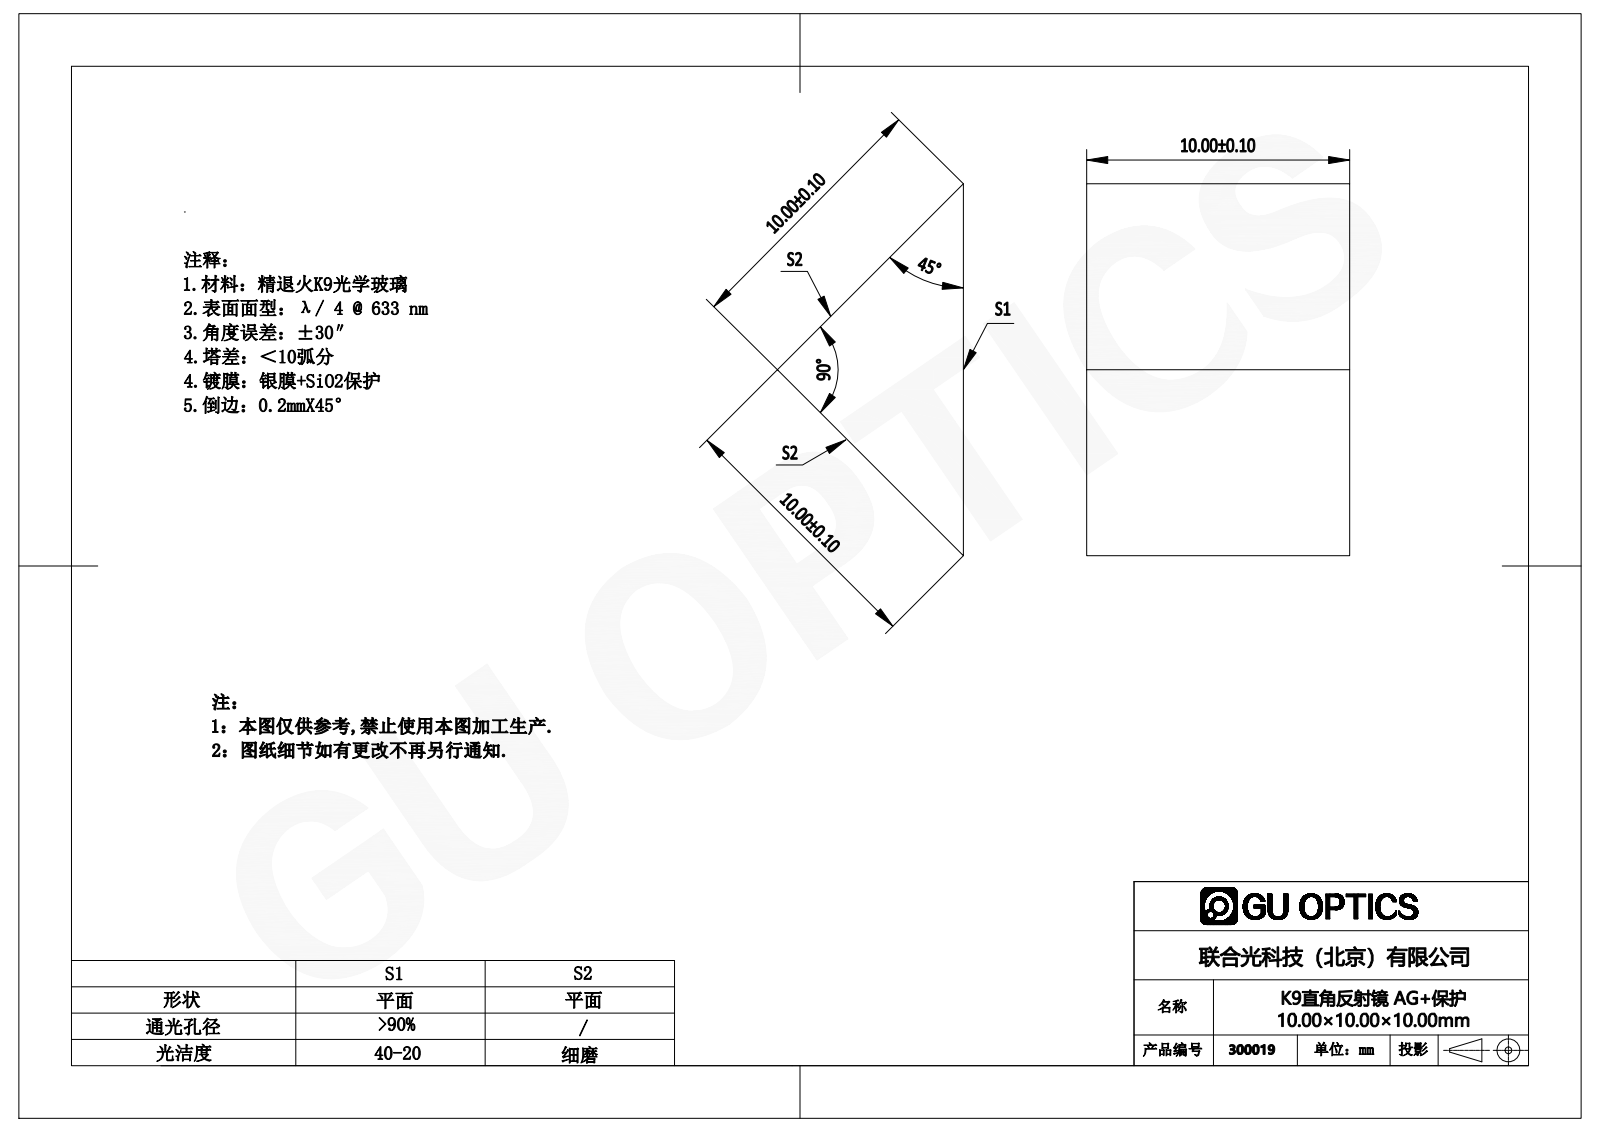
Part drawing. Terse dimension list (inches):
name: 300001
written by: SolidWorks 2016 (AUTOMOTIVE_DESIGN)
unit: in
bodies: 1 solid, 5 faces (5 planar, 0 cylindrical, 0 other)
size: 0.557 × 0.394 × 0.278
volume: 0.031 in³; area: 0.684 in²
face distances: 0.394
